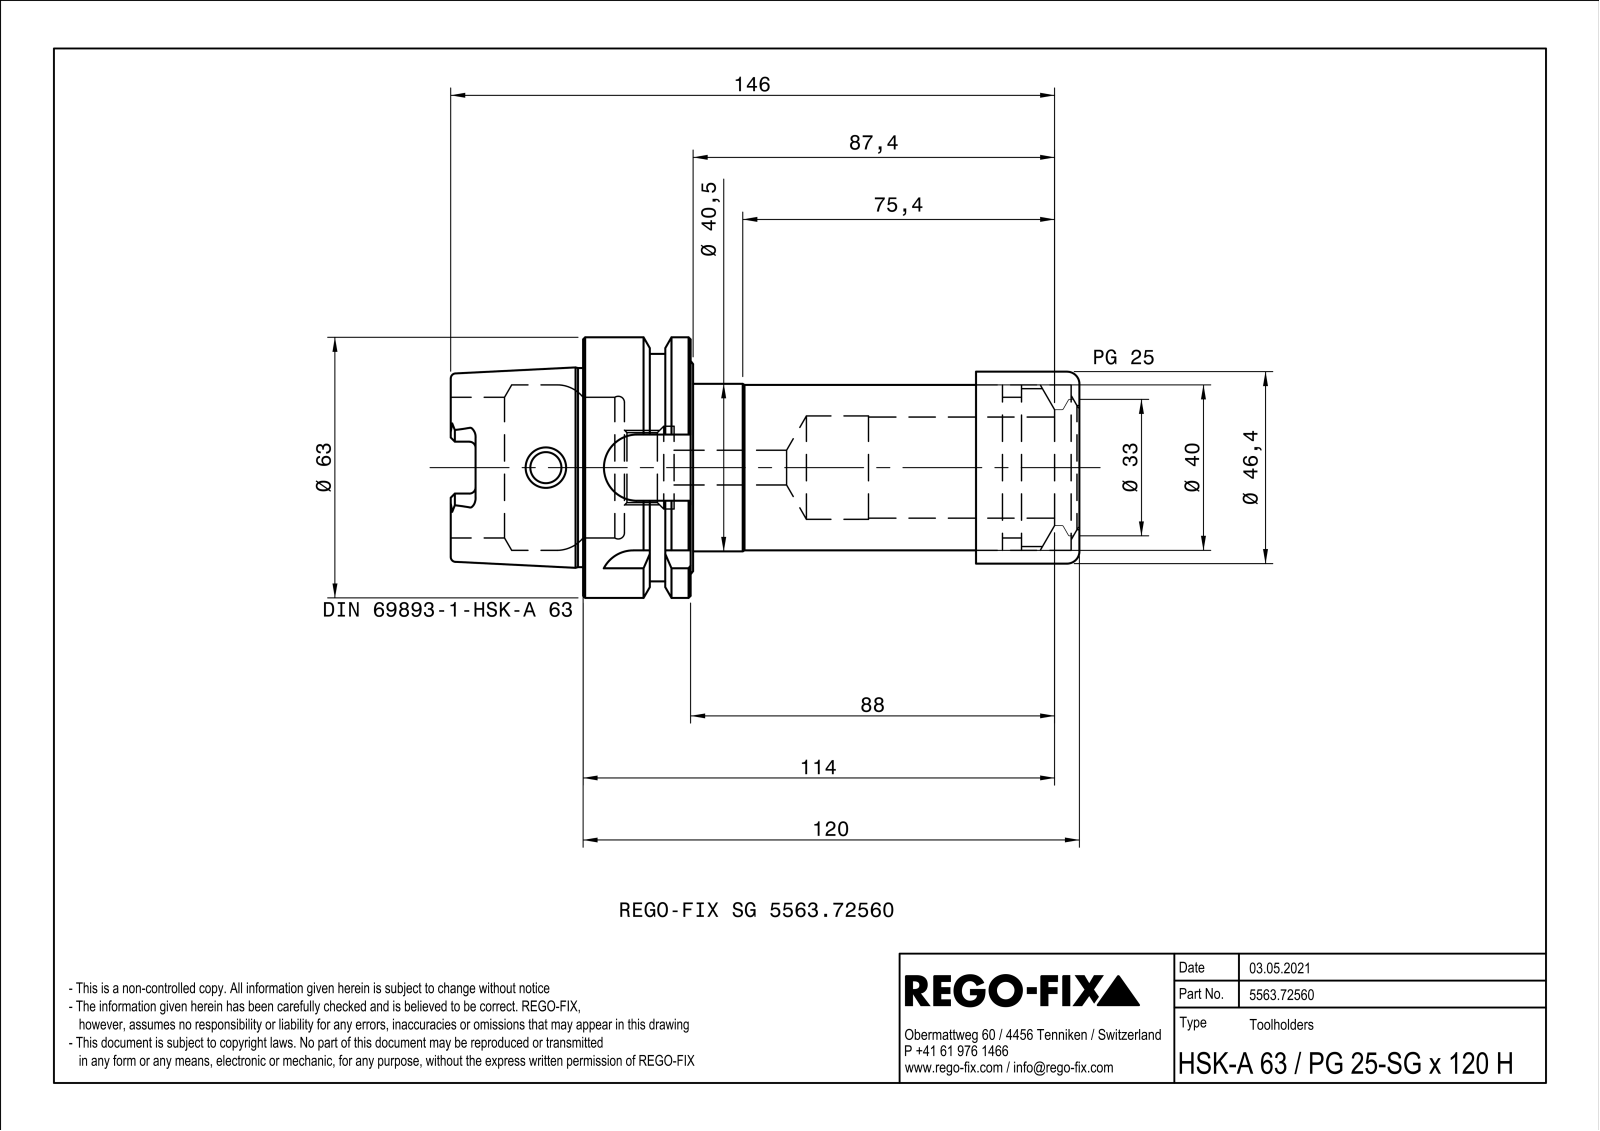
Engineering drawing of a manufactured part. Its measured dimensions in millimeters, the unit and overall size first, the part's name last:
Units: millimetres
Overall size (bounding box): 152 × 63 × 63
Round holes (diameter × count): ⌀7.5 ×1, ⌀8.4 ×1, ⌀8.5 ×1, ⌀10 ×1, ⌀16.92 ×1, ⌀20 ×1, ⌀25 ×1, ⌀30 ×1, ⌀34 ×1, ⌀38.38 ×1, ⌀40.05 ×1, ⌀42 ×1
Round bosses / shafts (diameter × count): ⌀63 ×1, ⌀55 ×1, ⌀48.13 ×1, ⌀46 ×1, ⌀40.5 ×1, ⌀40 ×1
Partial cylindrical surfaces — rounded edges, fillets, slot ends (radius × count): R1.5 ×6, R2.88 ×4, R8 ×4, R20.62 ×1, R22.38 ×1
Main face-to-face distances: 26, 16.6, 10, 16, 94, 120, 110, 93.4, 0.6, 26.6
Volume: 168 948 mm³ · Surface area: 47 309 mm²
Bodies: 2 solids, 160 faces (54 planar, 43 cylindrical, 63 other)
Part name (STEP PRODUCT): 0008429
STEP written by: SIEMENS PLM Software Solid Edge ST10 (AUTOMOTIVE_DESIGN)
